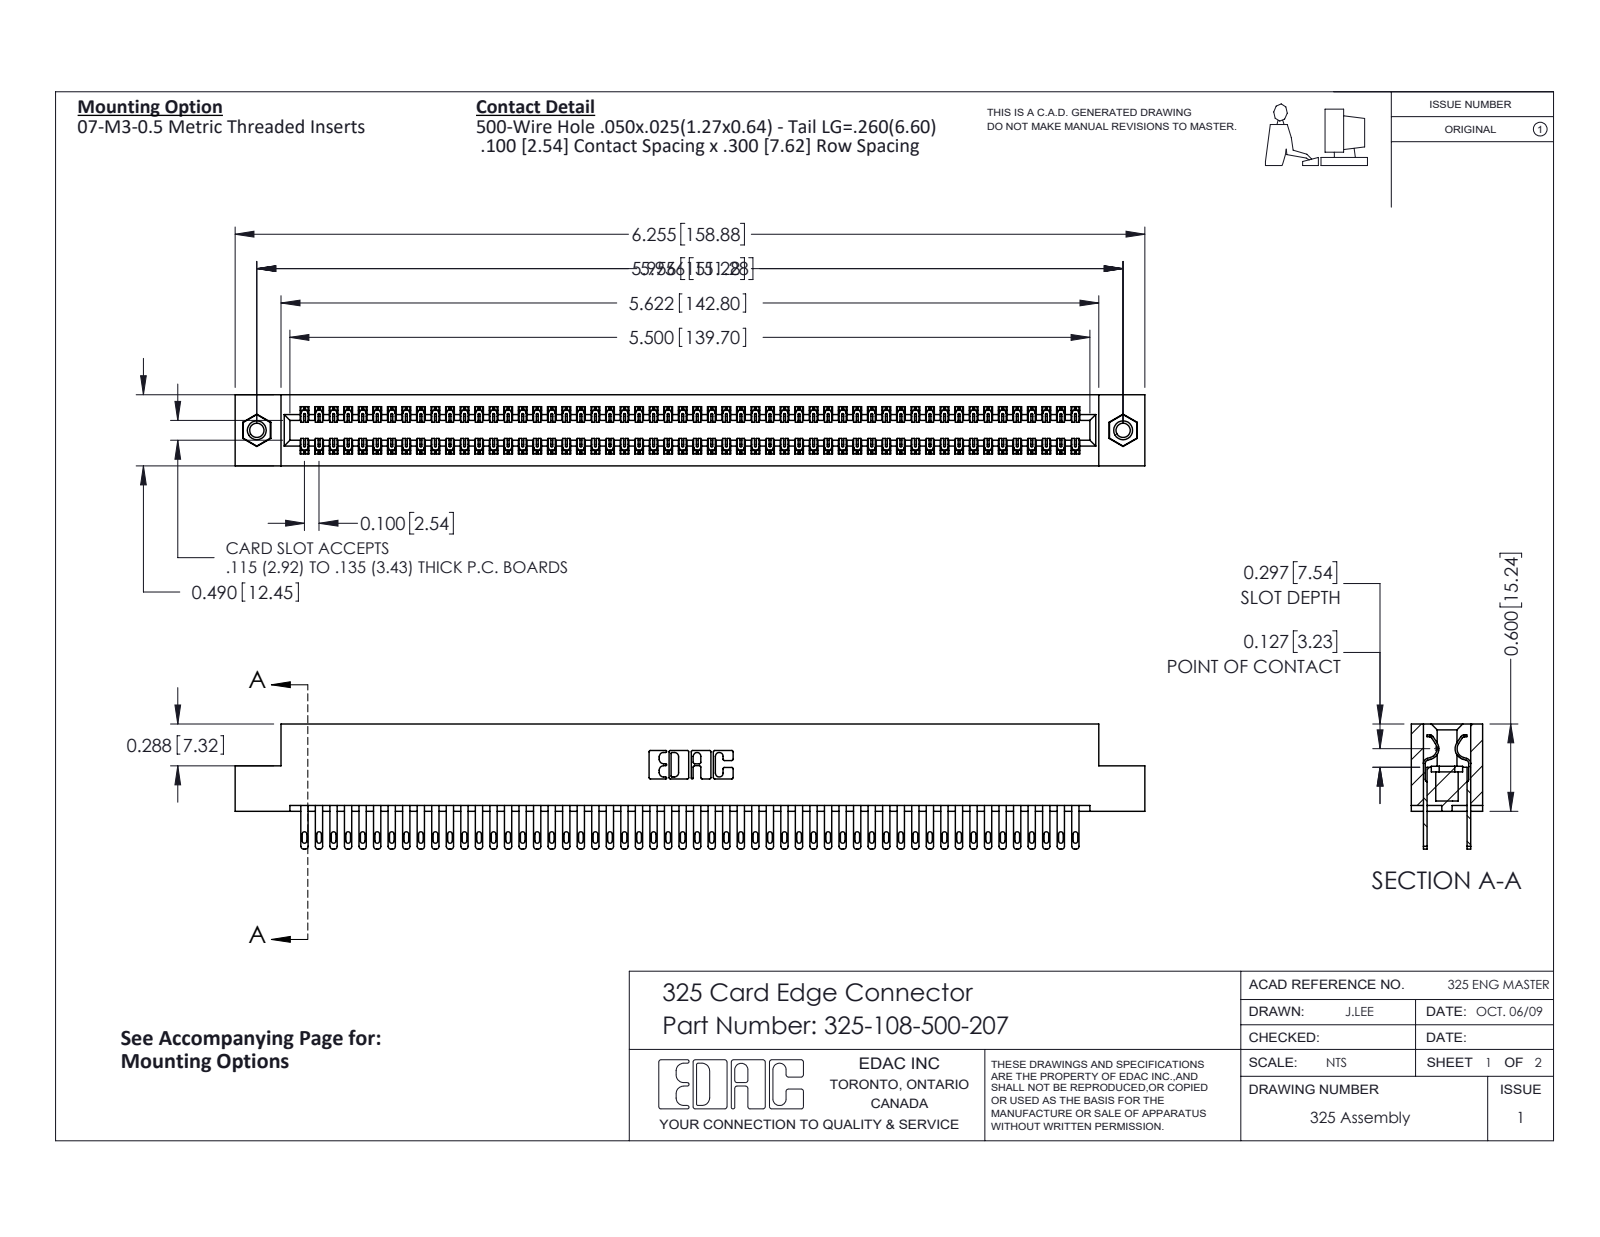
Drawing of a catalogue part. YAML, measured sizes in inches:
part_name: "345-250-001_345-250-005-103; 325-292-001_325-293-100; 325-108-500-207; 325 Part_TI"
step_written_by: "SolidWorks 2016 (CONFIG_CONTROL_DESIGN)"
units: inches
bodies: {solids: 111, faces: 5358, planar: 3342, cylindrical: 2000, other: 16}
overall_size: [6.255, 0.86, 0.49]
volume: 1.278
surface_area: 41.51
round_holes:
  - {diameter: 0.098, count: 2}
  - {diameter: 0.125, count: 2}
  - {diameter: 0.16, count: 2}
round_bosses_or_shafts:
  - {diameter: 0.155, count: 2}
partial_cylinders:
  - {radius: 0.006, count: 162}
  - {radius: 0.016, count: 108}
  - {radius: 0.02, count: 108}
  - {radius: 0.01, count: 22}
  - {radius: 0.007, count: 6}
  - {radius: 0.031, count: 6}
  - {radius: 0.026, count: 3}
  - {radius: 0.014, count: 2}
face_to_face_distances: [0.083, 0.407, 0.3, 0.107, 0.383, 0.025, 0.49, 0.325, 0.275, 0.56]
hole_center_spacings: [5.956]
